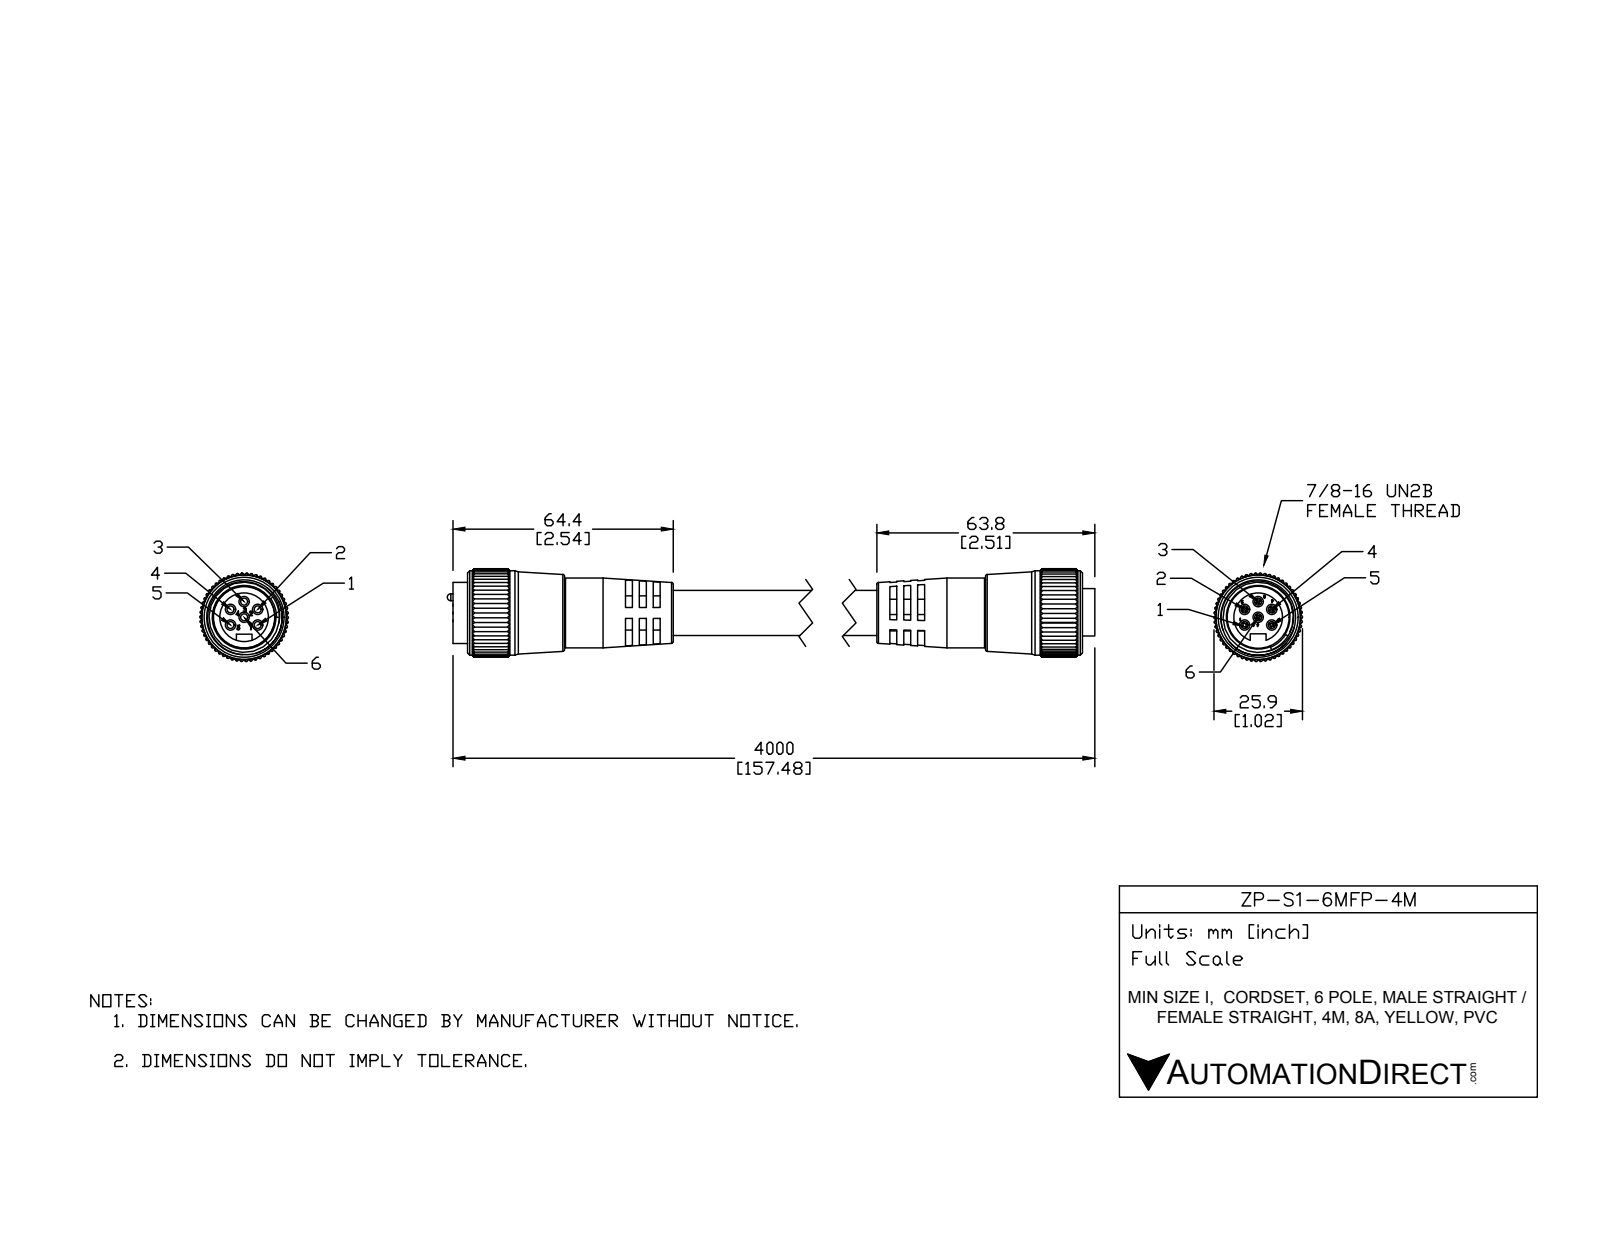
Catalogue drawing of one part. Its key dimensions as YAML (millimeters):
part_name: "ZP-S1-6MFP-4M"
step_written_by: "SolidWorks 2015 (AUTOMOTIVE_DESIGN)"
units: millimeters
bodies: {solids: 10, faces: 1226, planar: 452, cylindrical: 636, other: 138}
overall_size: [229.66, 25.84, 25.83]
volume: 50878
surface_area: 23497
round_holes:
  - {diameter: 3.05, count: 6}
  - {diameter: 19.96, count: 1}
  - {diameter: 20.45, count: 1}
  - {diameter: 21, count: 1}
round_bosses_or_shafts:
  - {diameter: 2, count: 6}
  - {diameter: 24.68, count: 1}
  - {diameter: 20.4, count: 1}
  - {diameter: 19.5, count: 1}
  - {diameter: 17.88, count: 1}
  - {diameter: 14.22, count: 1}
  - {diameter: 9.91, count: 1}
  - {diameter: 3.05, count: 1}
partial_cylinders:
  - {radius: 0.25, count: 165}
  - {radius: 2.29, count: 1}
  - {radius: 5.25, count: 1}
  - {radius: 12.93, count: 1}
face_to_face_distances: [2, 4.02, 117.68, 113.65, 4.03, 125.74, 59.84, 4.04, 121.7, 121.72]
hole_center_spacings: [4.57, 4.56, 7.91, 7.92, 9.14]
